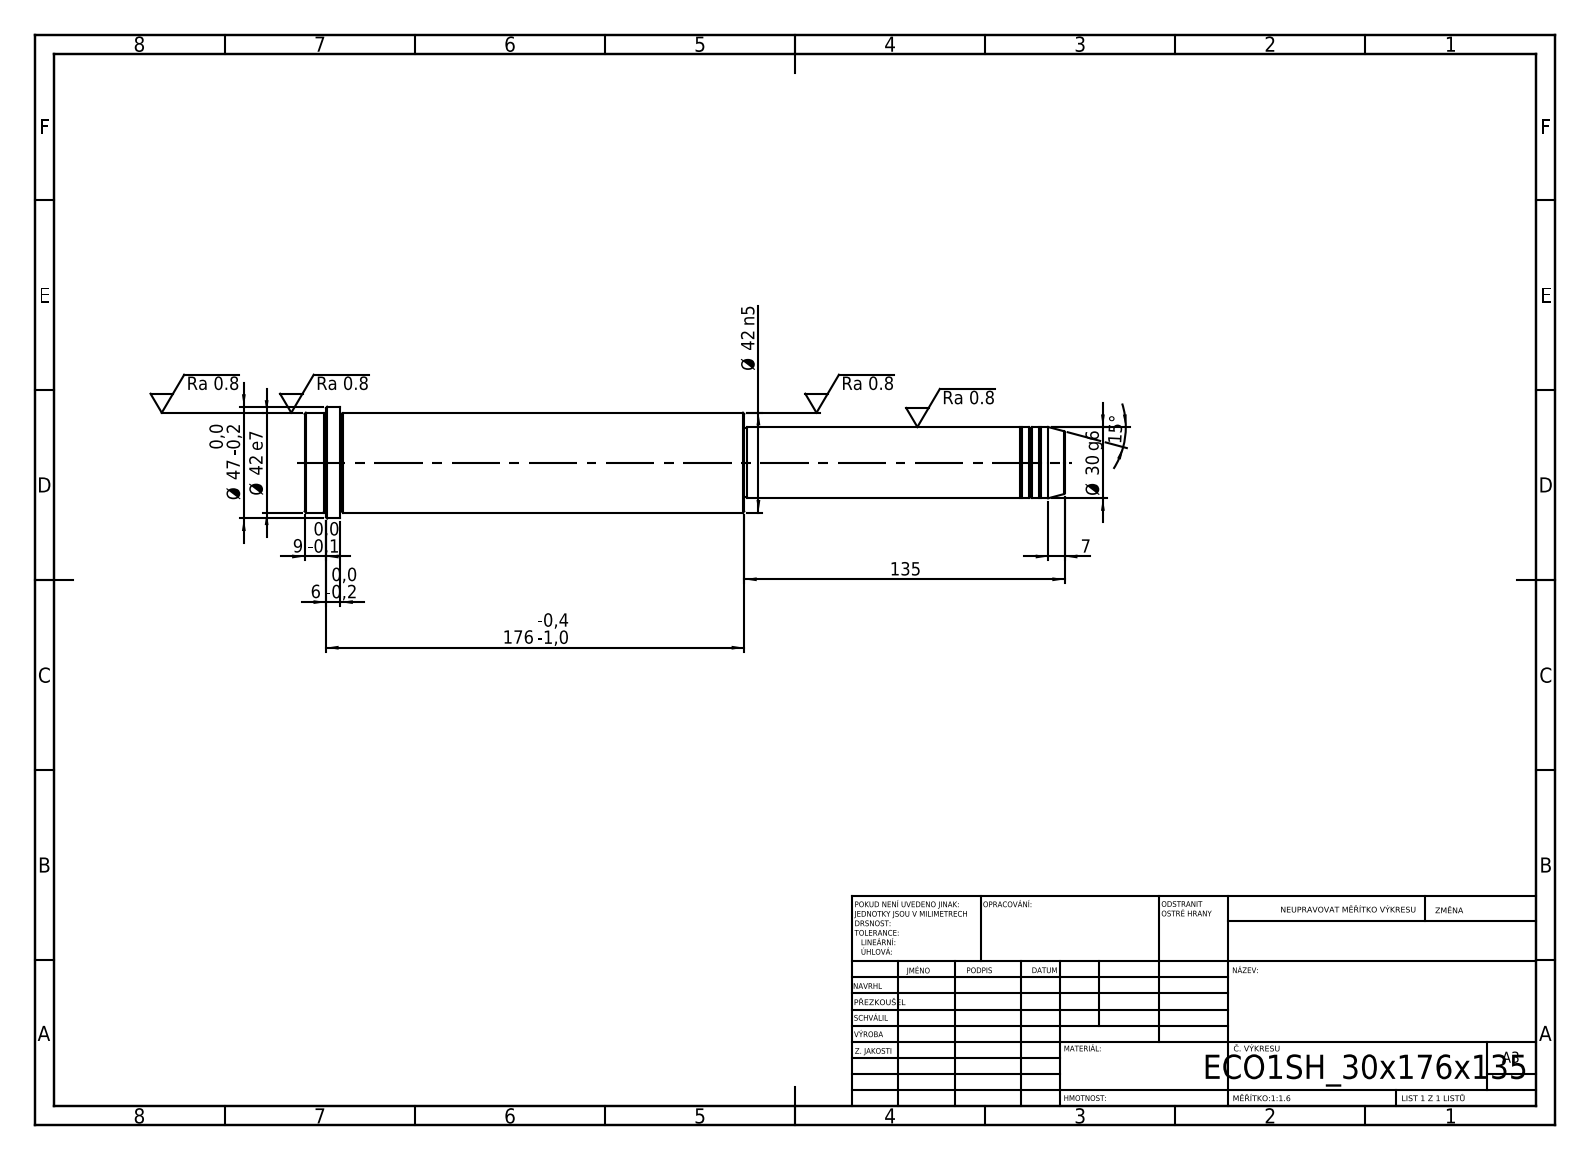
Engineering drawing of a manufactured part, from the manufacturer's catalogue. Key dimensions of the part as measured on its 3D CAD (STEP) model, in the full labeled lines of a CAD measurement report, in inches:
STEP written by: SolidWorks 2019 (CONFIG_CONTROL_DESIGN)
Units: inches
Bodies: 1 solid, 52 faces (6 planar, 16 cylindrical, 30 other)
Overall size (bounding box): 12.598 × 1.85 × 1.85
Volume: 21.54 in³ · Surface area: 63.19 in²
Round bosses / shafts (diameter × count): ⌀1.85 ×1, ⌀1.654 ×1, ⌀1.181 ×1, ⌀1.142 ×1
Main face-to-face distances: 7.283, 5.315, 12.598, 12.008, 6.693, 0.591, 12.244, 6.929, 0.236, 0.354
